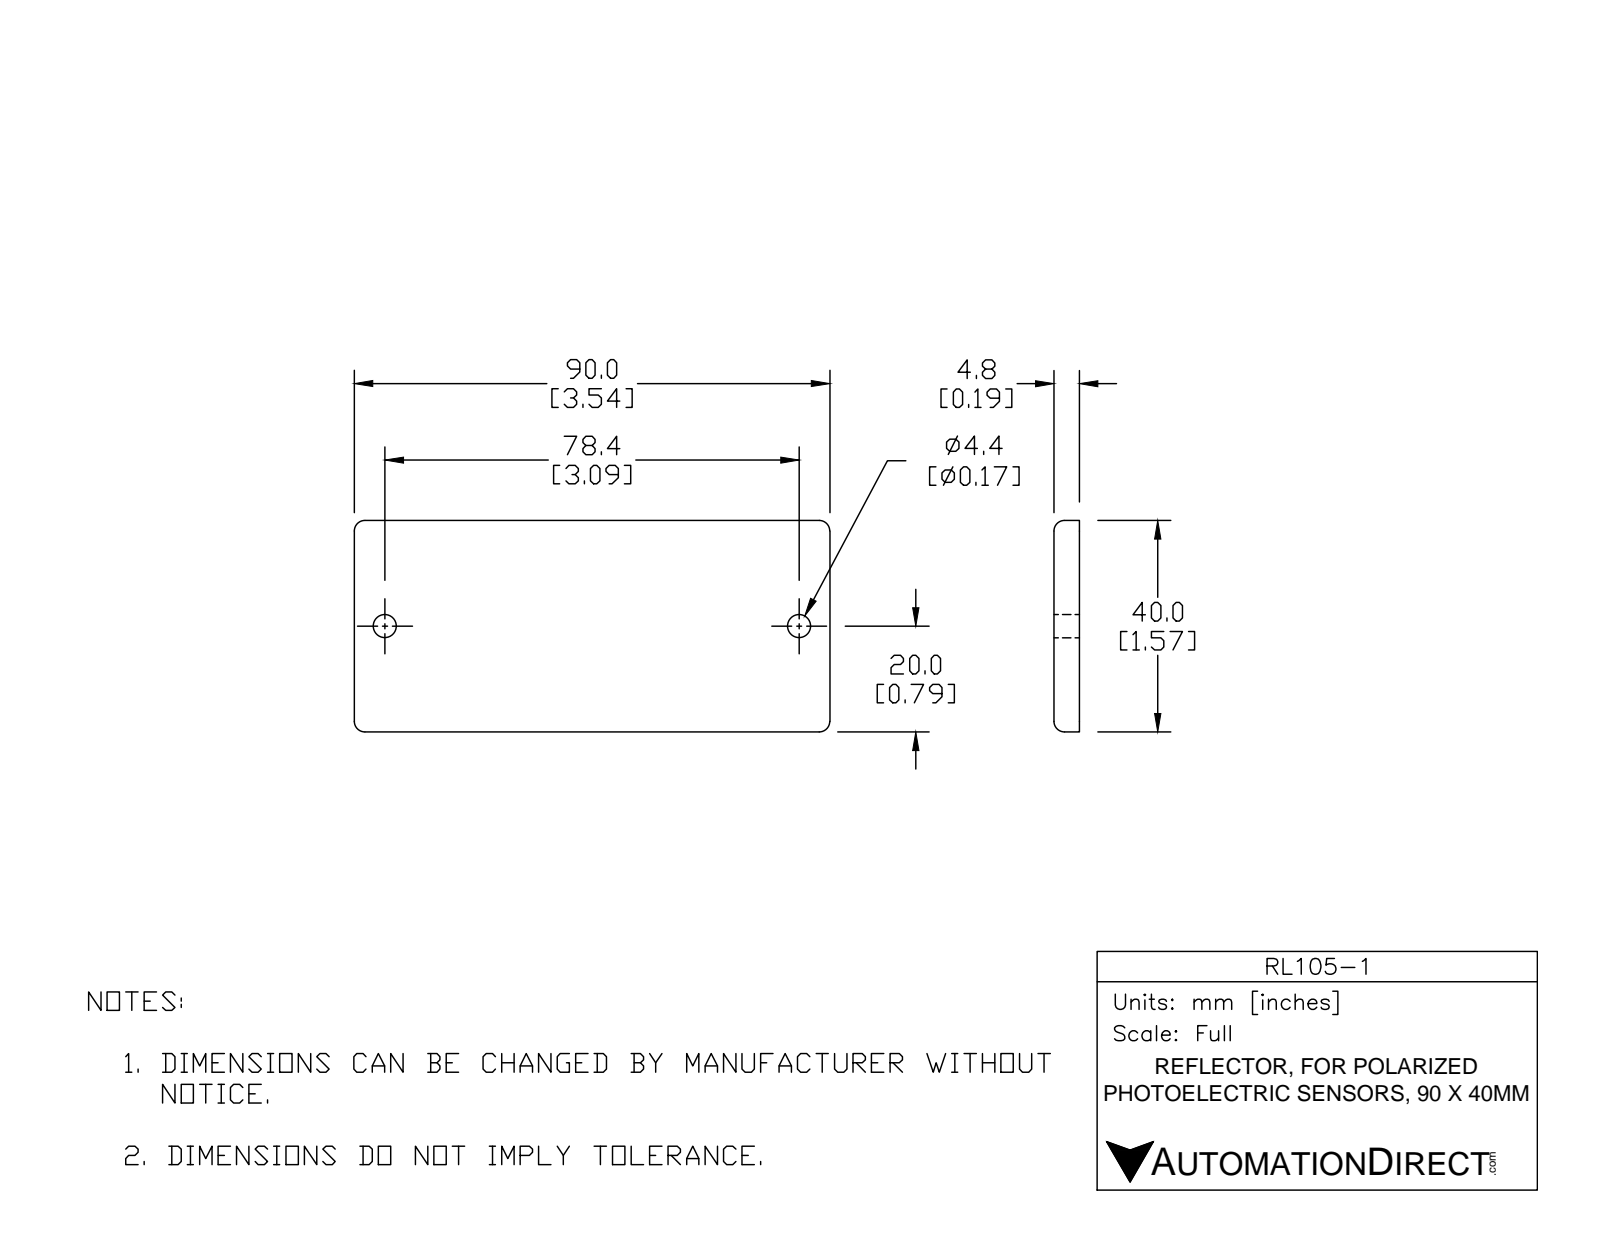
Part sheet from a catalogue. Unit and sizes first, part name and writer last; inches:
Units: inches
Overall size (bounding box): 3.543 × 1.575 × 0.189
Round holes (diameter × count): ⌀0.173 ×2
Partial cylindrical surfaces — rounded edges, fillets, slot ends (radius × count): R0.079 ×8
Main face-to-face distances: 0.189, 1.575, 3.543
Hole centre spacings: 3.087
Volume: 1.031 in³ · Surface area: 12.83 in²
Bodies: 1 solid, 22 faces (6 planar, 12 cylindrical, 4 other)
Part name (STEP PRODUCT): RL105-1
STEP written by: SolidWorks 2017 (AUTOMOTIVE_DESIGN)
